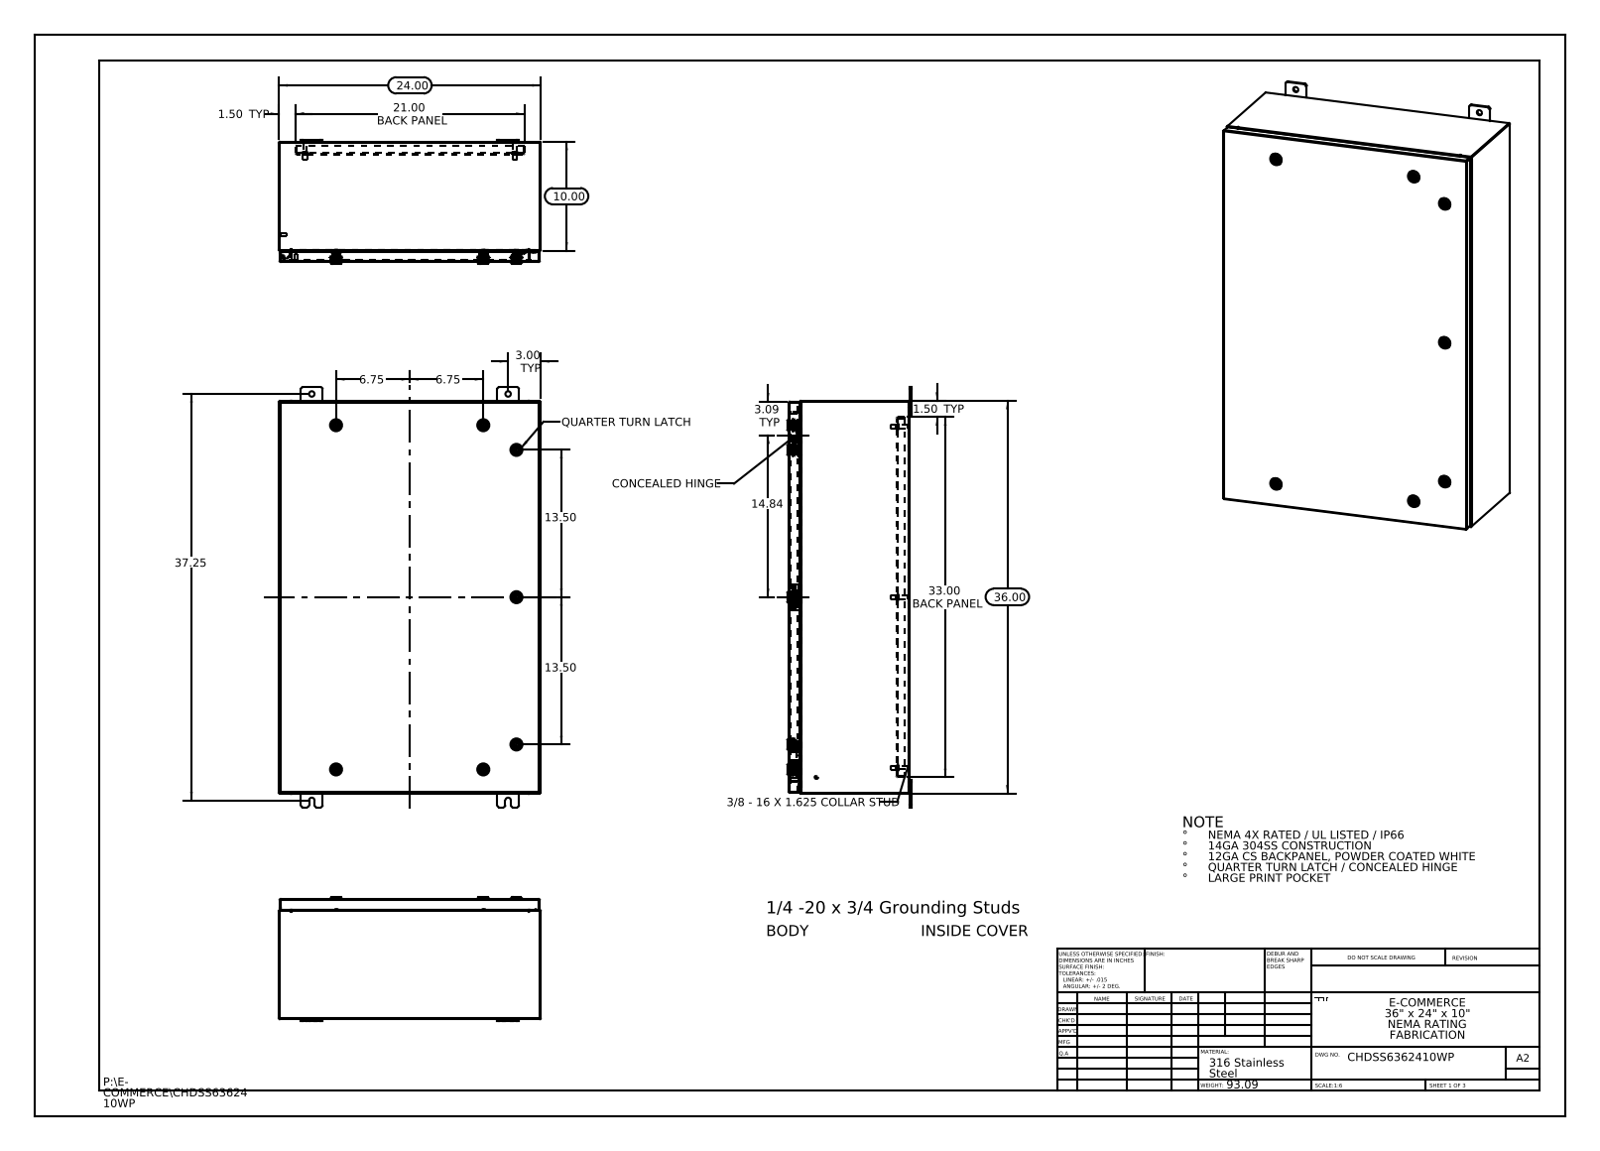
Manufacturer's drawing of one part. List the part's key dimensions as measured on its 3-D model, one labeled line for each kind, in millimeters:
Part name (STEP PRODUCT): CHDSS6362410WP Top; Concealed Hinge enclosure side; CHDSS6362410WP Body; Concealed Hinge (Cover Side) (+8 more)
STEP written by: SolidWorks 2013 (CONFIG_CONTROL_DESIGN)
Units: millimetres
Bodies: 65 solids, 6356 faces (1866 planar, 1988 cylindrical, 2502 other)
Overall size (bounding box): 977.9 × 609.6 × 288.4
Volume: 5 414 000 mm³ · Surface area: 5 302 000 mm²
Round holes (diameter × count): ⌀12.7 ×10, ⌀5 ×7, ⌀10 ×7, ⌀10.2 ×7, ⌀16 ×7, ⌀20 ×7, ⌀3.5 ×6, ⌀5.4 ×1
Round bosses / shafts (diameter × count): ⌀6 ×9, ⌀28 ×7, ⌀19.8 ×7, ⌀15.9 ×7, ⌀15.5 ×7, ⌀13.5 ×7, ⌀10 ×7, ⌀2.9 ×7
Partial cylindrical surfaces — rounded edges, fillets, slot ends (radius × count): R0.2 ×231, R3 ×231, R0.7 ×84, R0.5 ×28, R5 ×28, R4.8 ×24, R0.3 ×22, R2.2 ×18
Main face-to-face distances: 1.9, 1.9, 279.7, 277.7, 277.8, 275.9, 2.6, 607.7, 25.4, 27.3
Hole centre spacings: 342.9, 396.9, 629.7, 489, 17.5, 47.2, 54.1, 77.9
